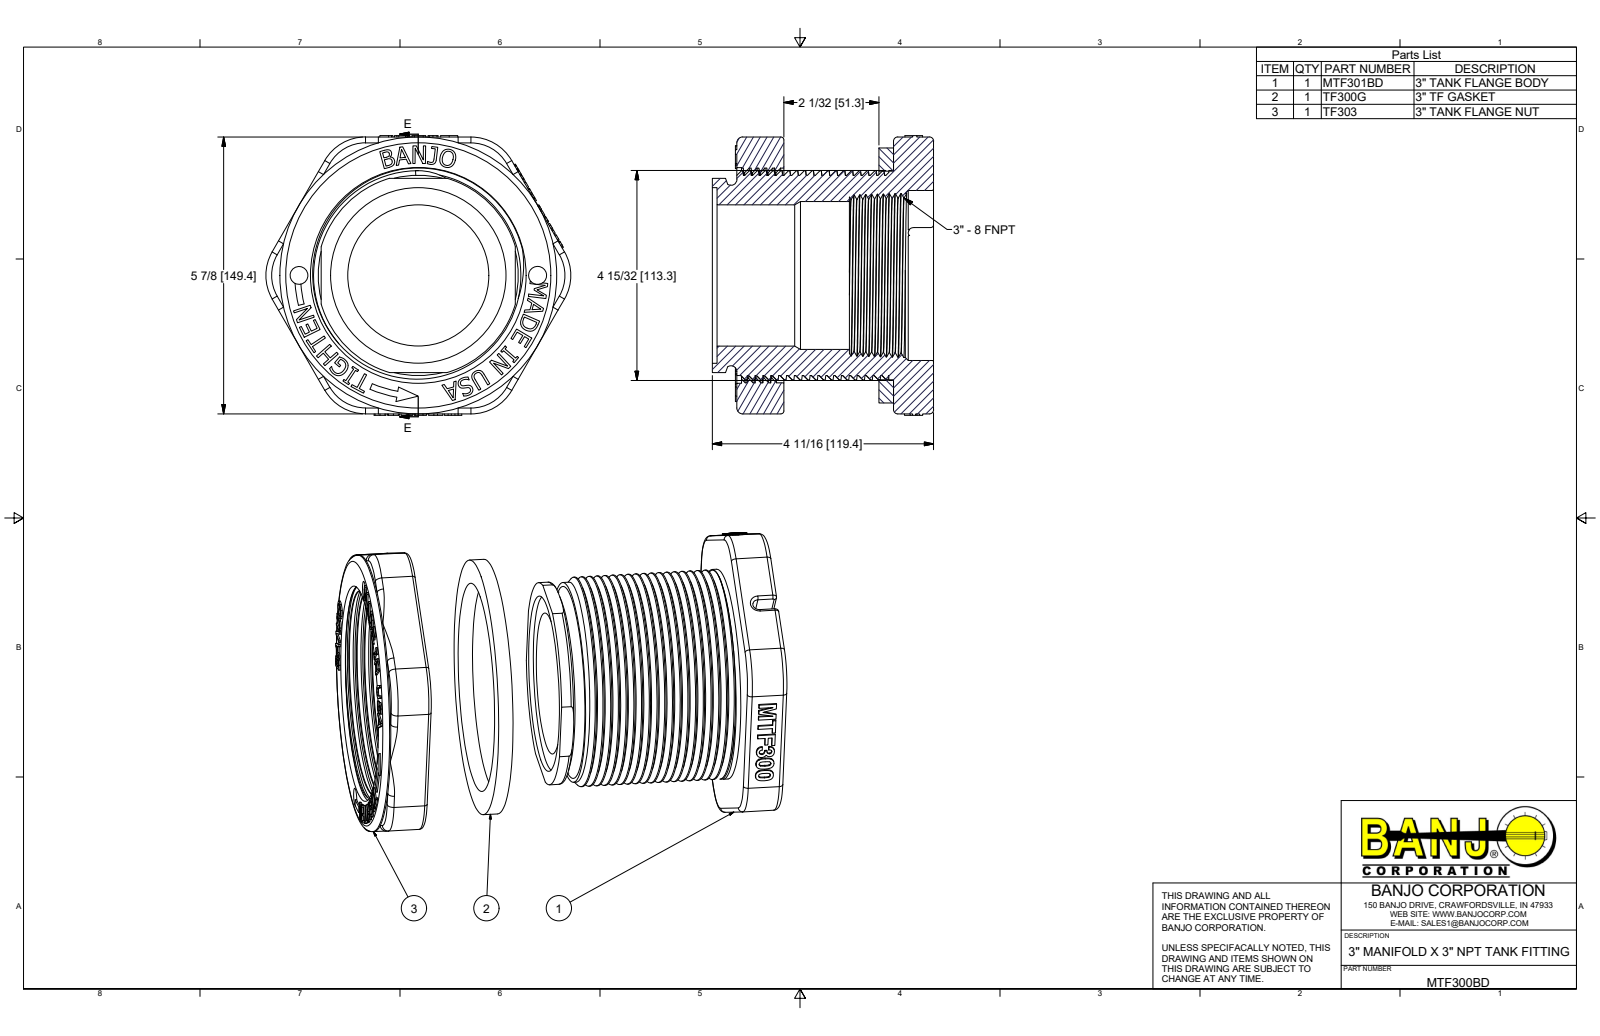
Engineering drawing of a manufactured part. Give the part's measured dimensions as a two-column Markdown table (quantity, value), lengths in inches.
| quantity | value |
| --- | --- |
| part name | MTF300BD; MTF301BD; TF300G; TF303 (+1 more) |
| STEP written by | Autodesk Inventor 2017 (AUTOMOTIVE_DESIGN) |
| units | inches |
| bodies | 3 solids, 862 faces (498 planar, 90 cylindrical, 274 other) |
| overall size | 6.48 × 5.942 × 4.7 |
| volume | 57.85 in³ |
| surface area | 302.4 in² |
| round holes (diameter × count) | 0.38 × 2, 3 × 1, 3.14 × 1, 3.61 × 1, 3.73 × 1, 4.361 × 1, 4.43 × 1, 4.561 × 1, 4.58 × 1 |
| round bosses / shafts (diameter × count) | 5.88 × 1, 5.416 × 1, 4.46 × 1, 4.45 × 1, 4.25 × 1 |
| partial cylindrical surfaces (radius × count) | 0.09 × 12, 0.125 × 7, 0.06 × 6, 0.063 × 6, 1 × 6, 0.03 × 4, 0.823 × 1, 1.163 × 1 |
| main face-to-face distances | 0.85, 3.18, 2.33, 1, 3.33, 4.18, 0.31, 3.02, 2.02, 1.16 |
| hole center spacings | 2.535, 5.07 |
